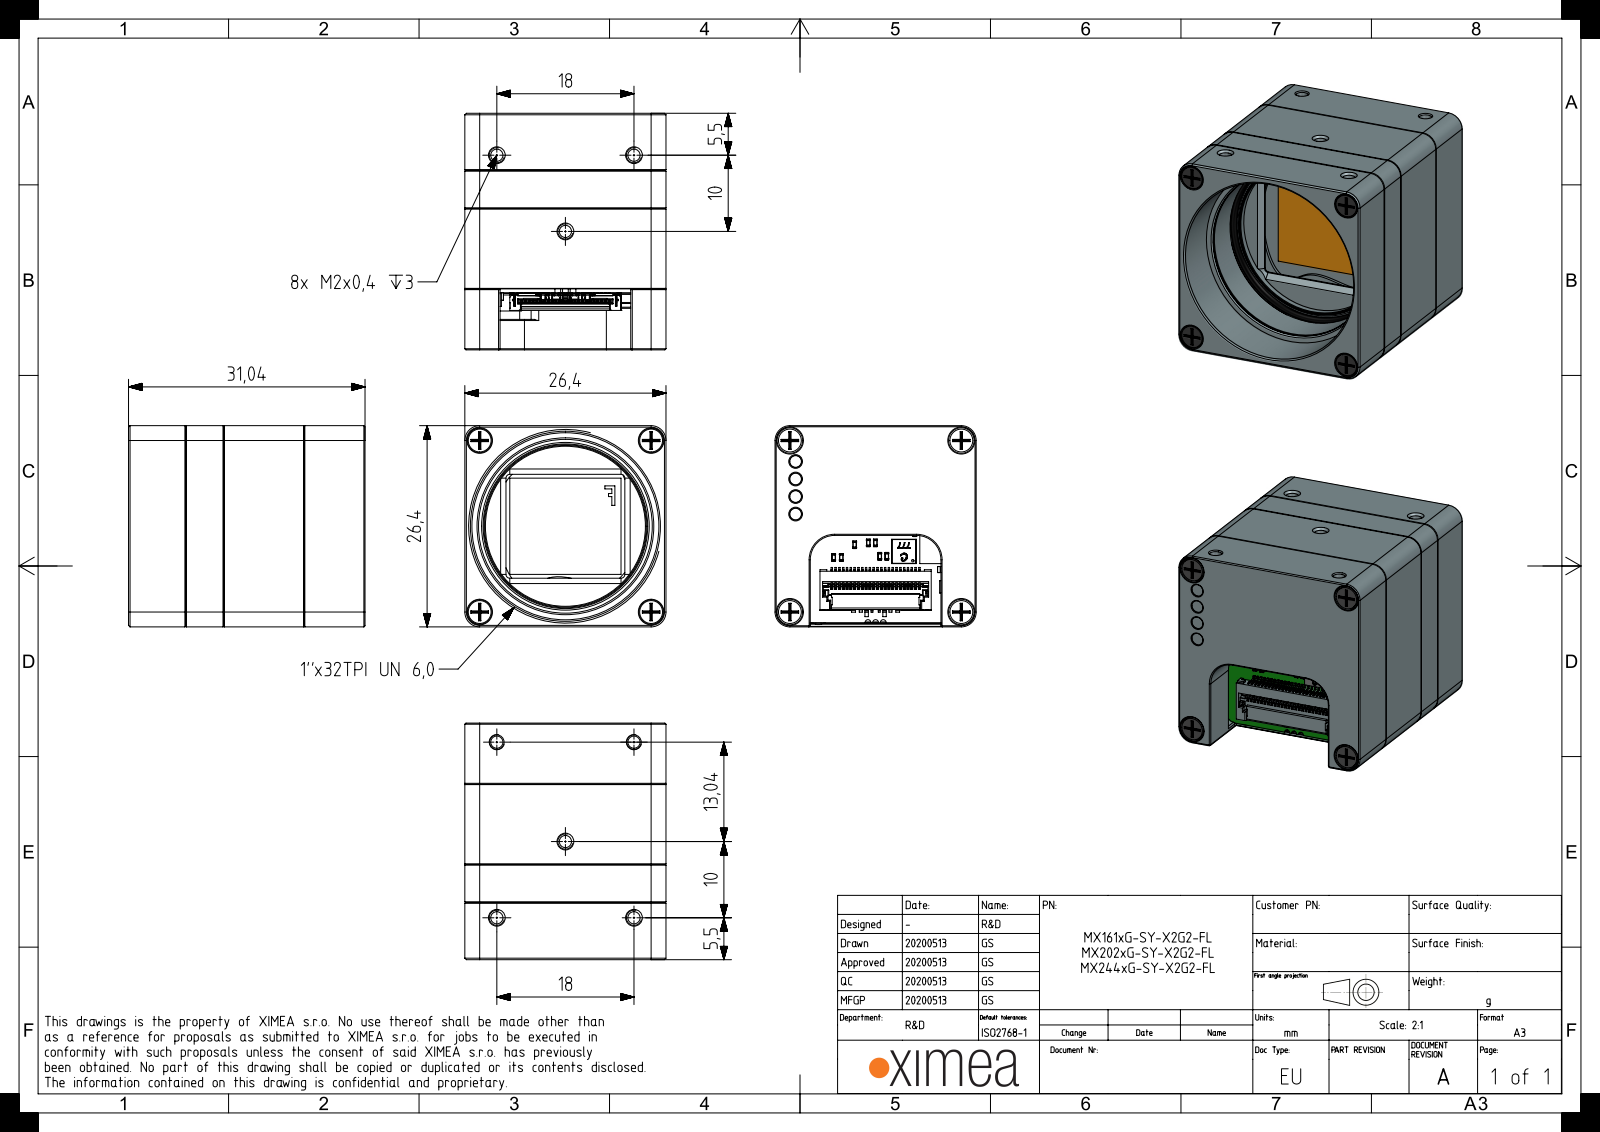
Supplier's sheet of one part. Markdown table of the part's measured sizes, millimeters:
| quantity | value |
| --- | --- |
| part name | MECH-MX-THERMAL-PAD-10X10; MECH-LIGHTPIPE-1.63x4.14; MX-X2G2-MAIN-FV-PCA-LW; MECH-MX-X2G2-REAR (+8 more) |
| STEP written by | SIEMENS PLM Software NX 1907 (AUTOMOTIVE_DESIGN) |
| units | millimeters |
| bodies | 31 solids, 7048 faces (5112 planar, 1674 cylindrical, 262 other) |
| overall size | 31 × 26.4 × 26.4 |
| volume | 10 400 mm³ |
| surface area | 17 940 mm² |
| round holes (diameter × count) | 1.6 × 13, 0.9 × 4, 2 × 4, 2.1 × 4, 3 × 4, 3.2 × 4, 3.4 × 4, 1.3 × 2, 1.7 × 2, 21 × 1, 22.8 × 1, 24.4 × 1 |
| round bosses / shafts (diameter × count) | 1.9 × 4, 1.6 × 4, 0.8 × 4, 3 × 2, 1.6 × 2, 25 × 1, 21.6 × 1 |
| partial cylindrical surfaces (radius × count) | 0.4 × 18, 0.3 × 16, 1.5 × 15, 0.2 × 14, 0.5 × 12, 1 × 12, 0.3 × 8, 1.3 × 8 |
| main face-to-face distances | 26.4, 1, 11.6, 3.6, 8.1, 2.6, 10.6, 10.5, 4.6, 3.6 |
| hole center spacings | 15.9, 22.5, 2.3, 3.8, 4.6, 13.5, 13.5, 15.8 |
